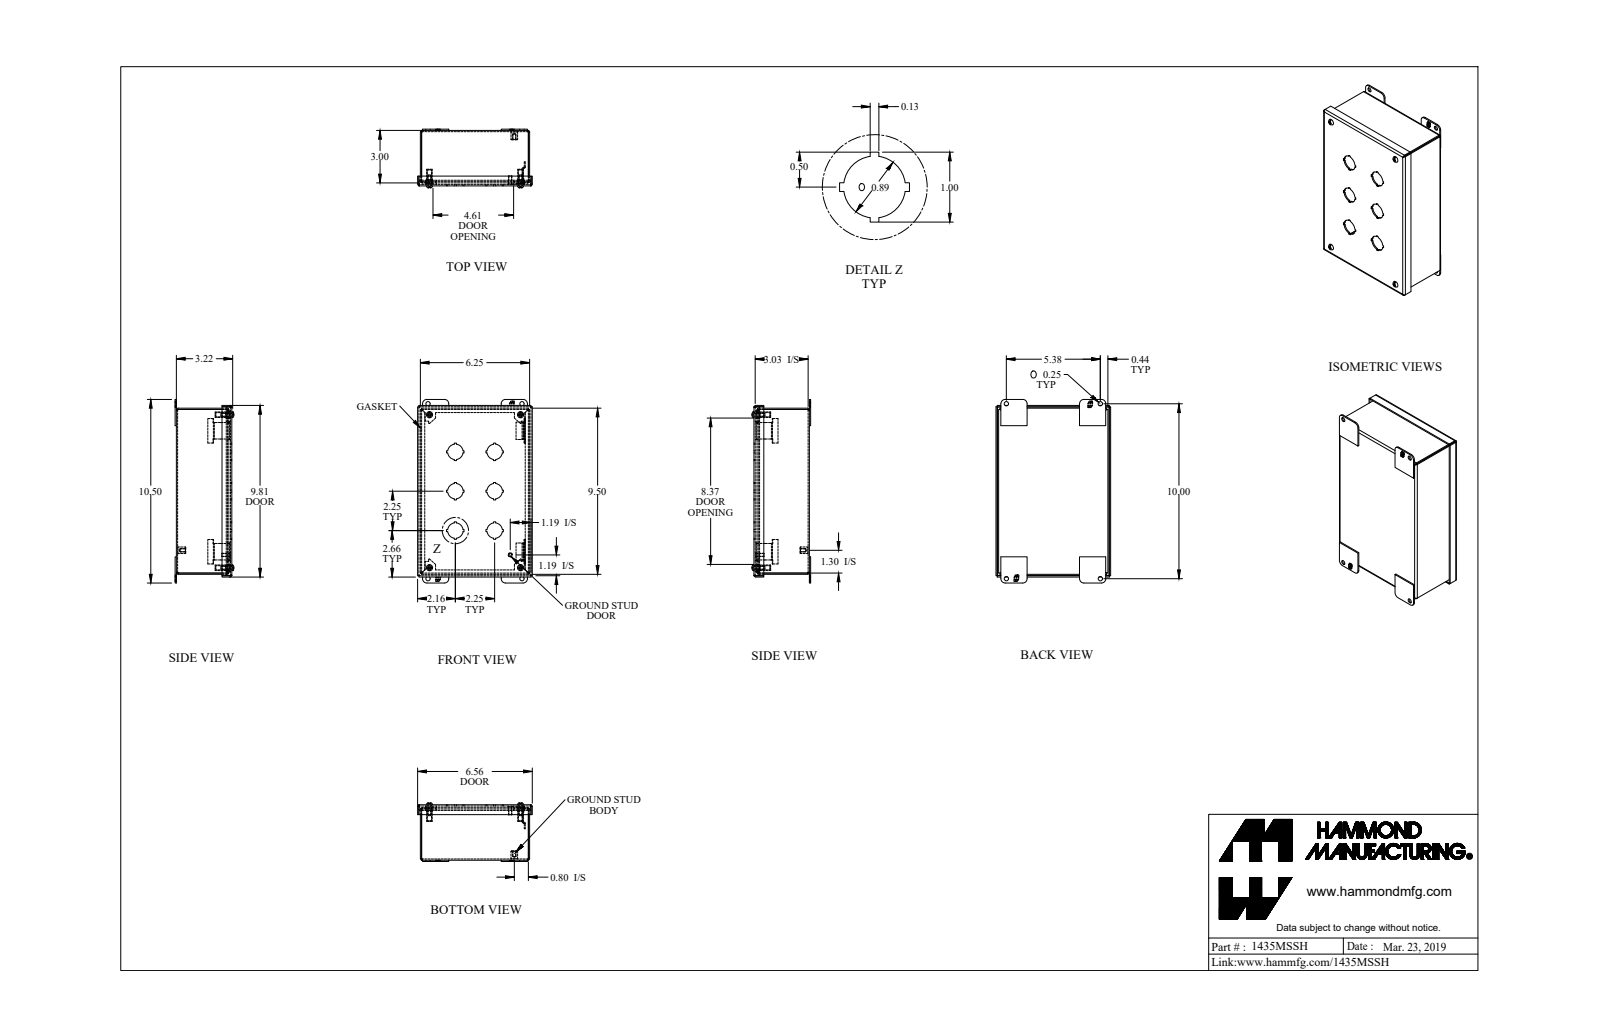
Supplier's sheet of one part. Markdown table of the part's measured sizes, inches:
| quantity | value |
| --- | --- |
| part name | 1435MSSH_Default |
| STEP written by | SolidWorks 2019 (CONFIG_CONTROL_DESIGN) |
| units | inches |
| bodies | 23 solids, 701 faces (495 planar, 176 cylindrical, 30 other) |
| overall size | 10.5 × 6.562 × 3.354 |
| volume | 20.63 in³ |
| surface area | 546.6 in² |
| round holes (diameter × count) | 0.25 × 8, 0.886 × 6, 0.065 × 4, 0.239 × 4, 0.253 × 4, 0.406 × 4, 0.156 × 1 |
| round bosses / shafts (diameter × count) | 0.19 × 5, 0.406 × 4, 0.315 × 4, 0.148 × 4, 0.375 × 1, 0.25 × 1 |
| partial cylindrical surfaces (radius × count) | 0.036 × 12, 0.108 × 12, 0.25 × 8, 0.029 × 4, 0.086 × 4, 0.171 × 4 |
| main face-to-face distances | 0.072, 3.1, 3.172, 3.028, 6.178, 9.428, 6.25, 6.106, 0.156, 6.334 |
| hole center spacings | 5.211, 5.212, 8.749, 8.75, 9.375, 2.25, 10.183, 10.183 |
